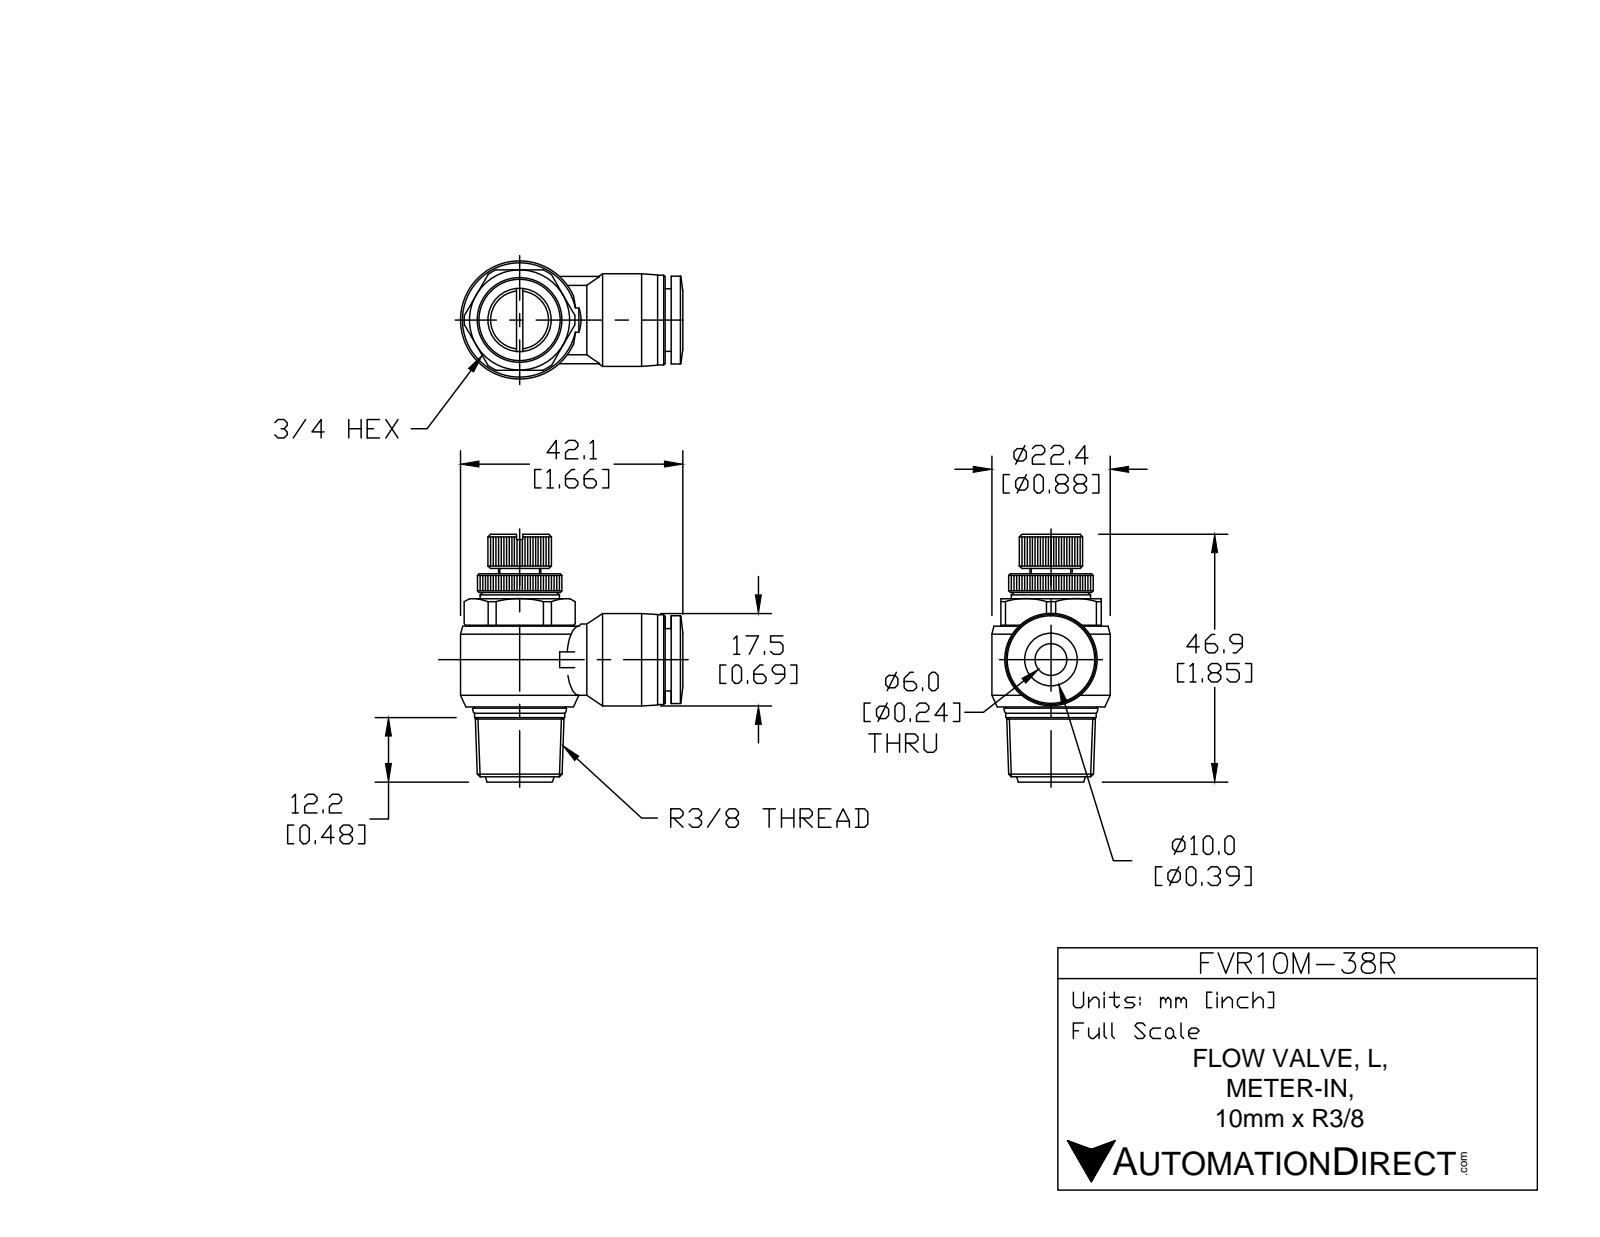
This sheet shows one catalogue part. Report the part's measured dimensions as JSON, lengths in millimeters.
{"part_name": "FVR10M-38R", "step_written_by": "SolidWorks 2015 (AUTOMOTIVE_DESIGN)", "units": "millimeters", "bodies": {"solids": 1, "faces": 569, "planar": 255, "cylindrical": 145, "other": 169}, "overall_size": [56.8, 42.1, 22.4], "volume_mm3": 14900, "surface_area_mm2": 6372, "round_holes": [[4.3, 2], [10.3, 1]], "round_bosses_or_shafts": [[22.4, 1], [19, 1], [17.5, 1], [17.1, 1], [17.1, 1], [17, 1], [16.6, 1], [15, 1]], "partial_cylinders_radius": [[6, 1], [8, 1], [10.5, 1]], "face_to_face_distances": [19, 26.3, 5.8, 34.7, 40.5, 15.3, 1.1, 14.2, 20.5, 29.5]}
